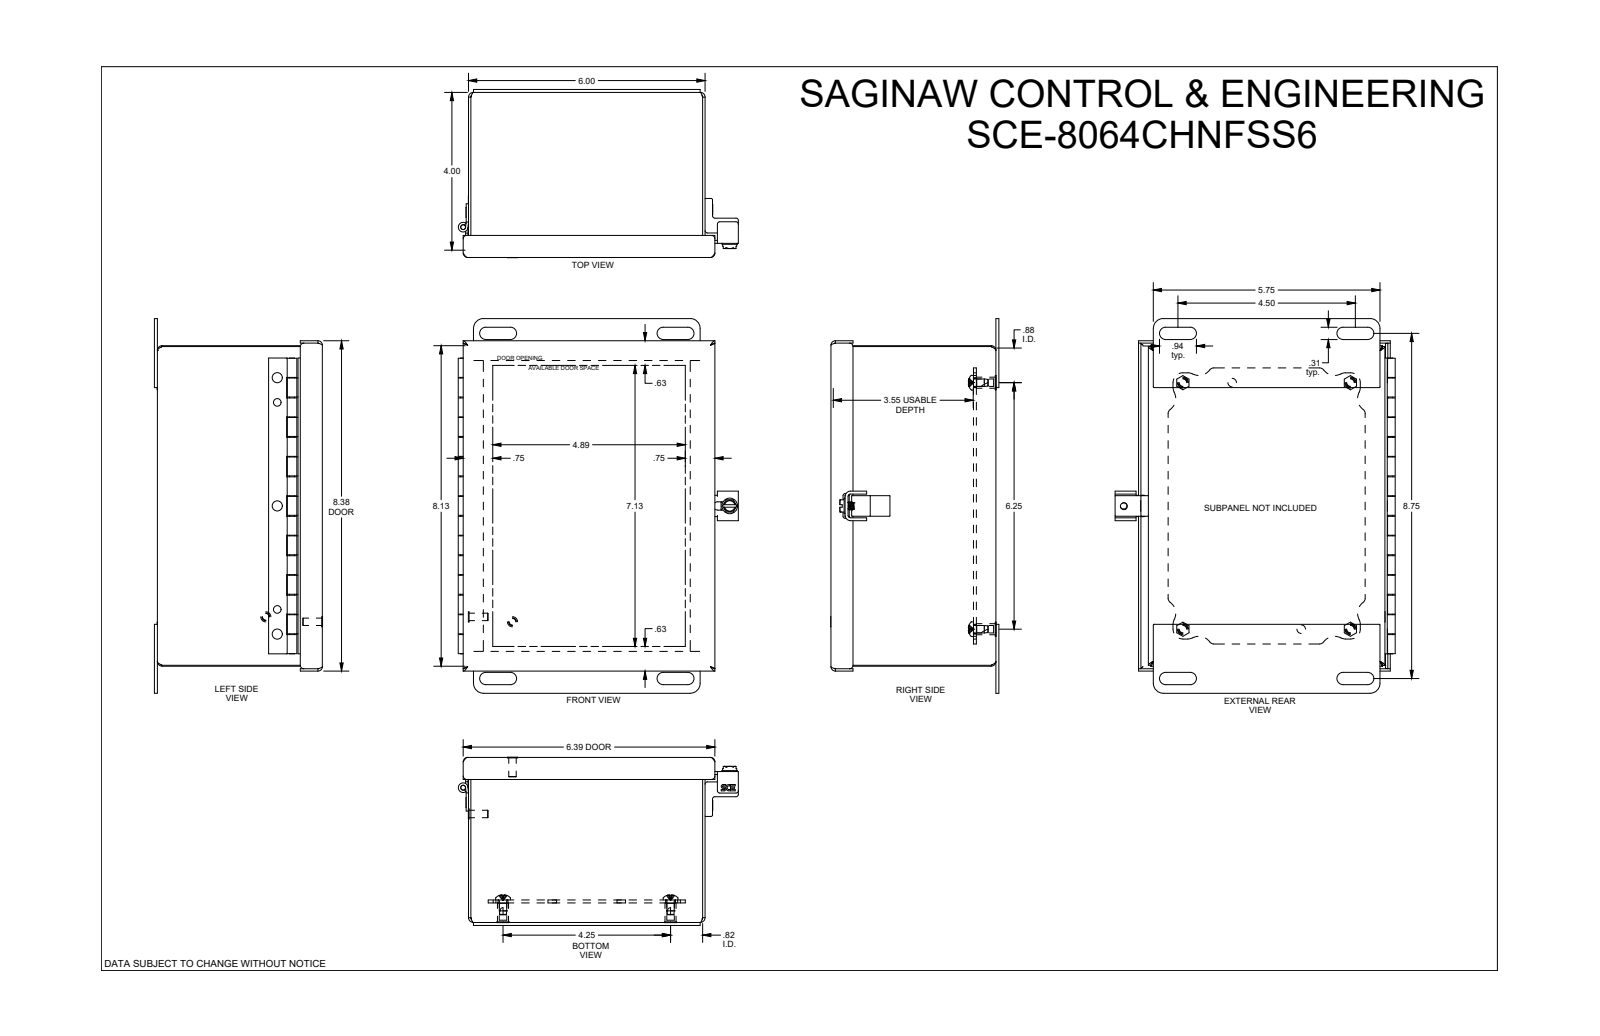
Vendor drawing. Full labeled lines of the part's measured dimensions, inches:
Part name (STEP PRODUCT): SCE-8064CHNFSS6
STEP written by: SolidWorks 2019 (CONFIG_CONTROL_DESIGN)
Units: inches
Bodies: 0 solids, 1097 faces (504 planar, 295 cylindrical, 298 other)
Overall size (bounding box): 9.5 × 7.104 × 4.265
Round holes (diameter × count): ⌀0.19 ×8, ⌀0.193 ×6, ⌀0.25 ×4, ⌀0.281 ×4, ⌀0.193 ×2, ⌀0.218 ×2, ⌀0.126 ×1, ⌀0.156 ×1, ⌀0.266 ×1
Round bosses / shafts (diameter × count): ⌀0.188 ×11, ⌀0.256 ×6, ⌀0.373 ×4, ⌀0.28 ×4, ⌀0.396 ×1, ⌀0.246 ×1, ⌀0.123 ×1
Partial cylindrical surfaces — rounded edges, fillets, slot ends (radius × count): R0.01 ×48, R0.06 ×17, R0.25 ×16, R0.007 ×8, R0.052 ×8, R0.112 ×8, R0.125 ×8, R0.156 ×8
Main face-to-face distances: 0.06, 0.06, 5.94, 4.125, 4.185, 4.065, 4.125, 0.075, 6, 3.63
Hole centre spacings: 1.25, 3, 3.25, 3.251, 4.25, 6.25, 6.374, 6.933
